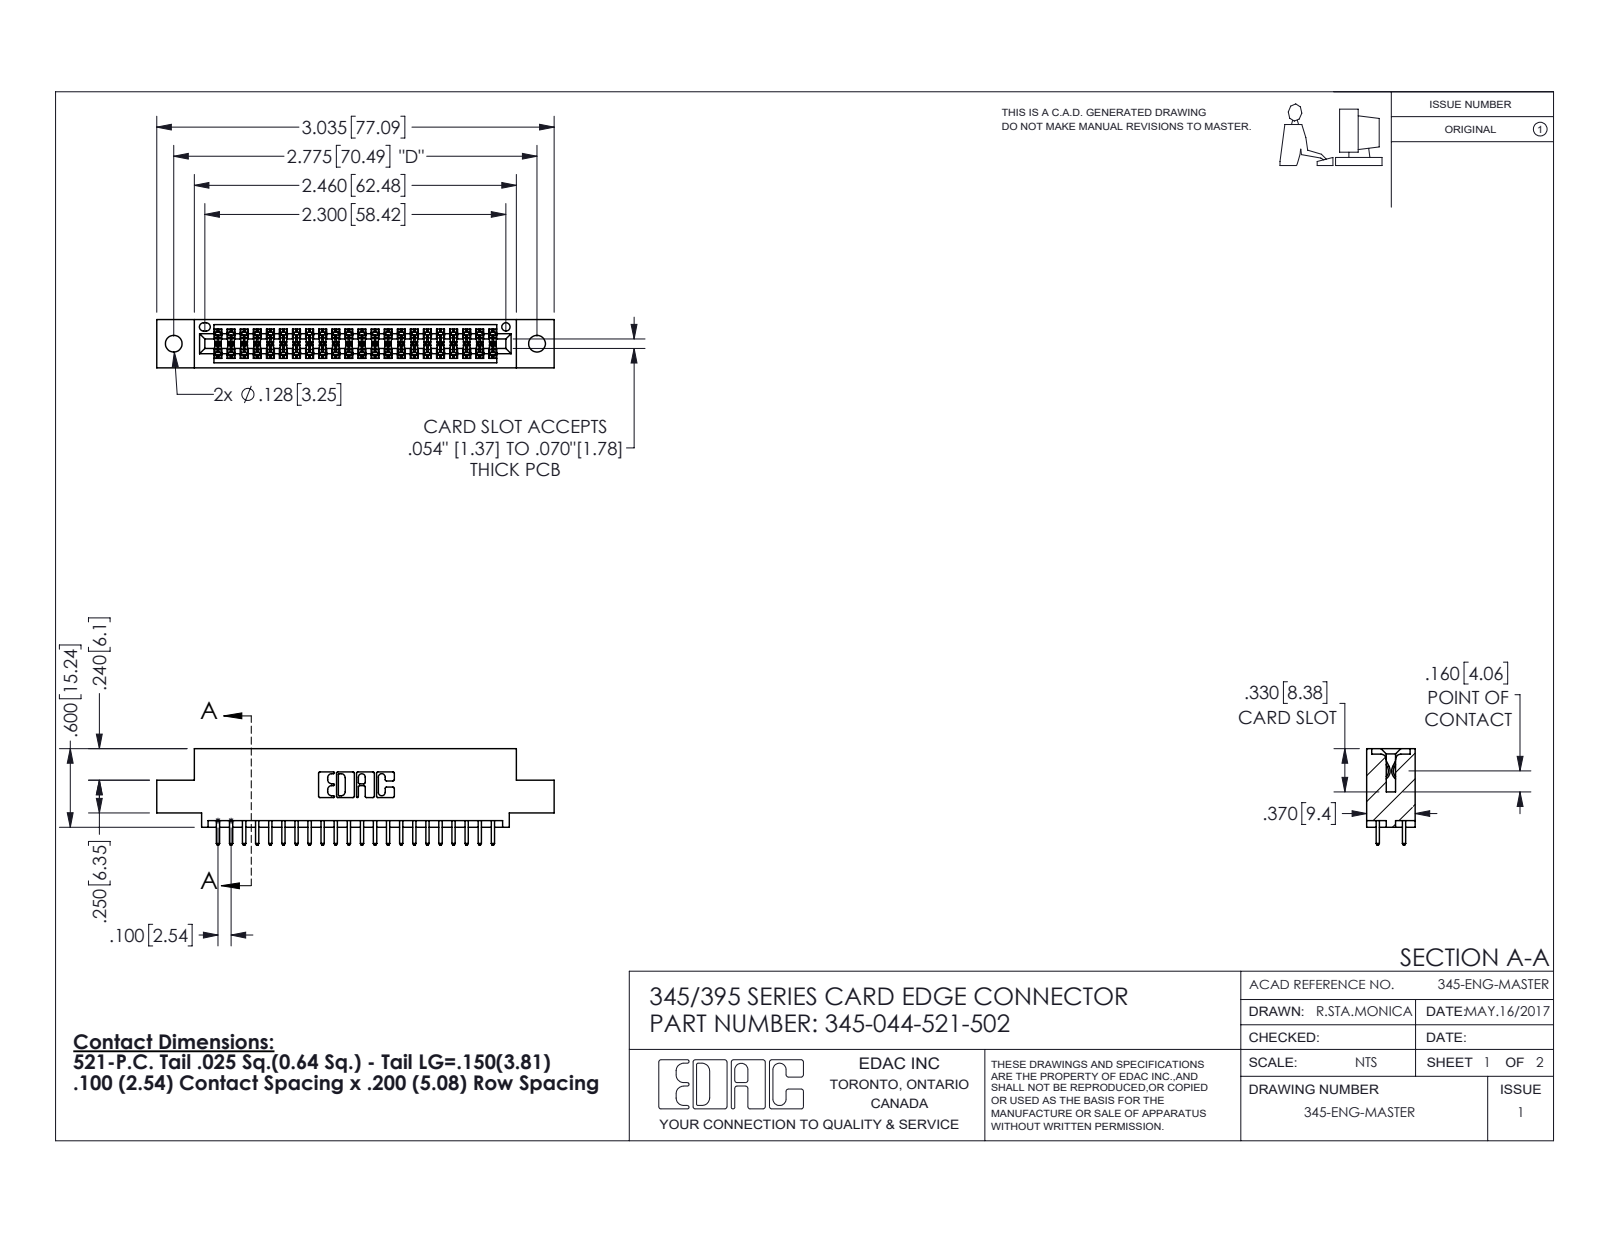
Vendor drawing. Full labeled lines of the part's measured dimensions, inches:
Part name (STEP PRODUCT): 345-292-001_345-293-121; 345-044-521-502; 345 Part_0.110 Offset - 0.128 Dia
STEP written by: SolidWorks 2016 (CONFIG_CONTROL_DESIGN)
Units: inches
Bodies: 45 solids, 2330 faces (1536 planar, 794 cylindrical, 0 other)
Overall size (bounding box): 3.035 × 0.737 × 0.37
Volume: 0.438 in³ · Surface area: 15.38 in²
Round holes (diameter × count): ⌀0.128 ×2, ⌀0.064 ×1
Partial cylindrical surfaces — rounded edges, fillets, slot ends (radius × count): R0.006 ×66, R0.01 ×44, R0.01 ×22, R0.007 ×6, R0.031 ×6, R0.026 ×3, R0.014 ×2, R0.019 ×2
Main face-to-face distances: 0.298, 0.072, 0.2, 0.37, 0.098, 0.272, 0.025, 0.225, 0.175, 0.149
Hole centre spacings: 0.27, 2.541, 2.775
